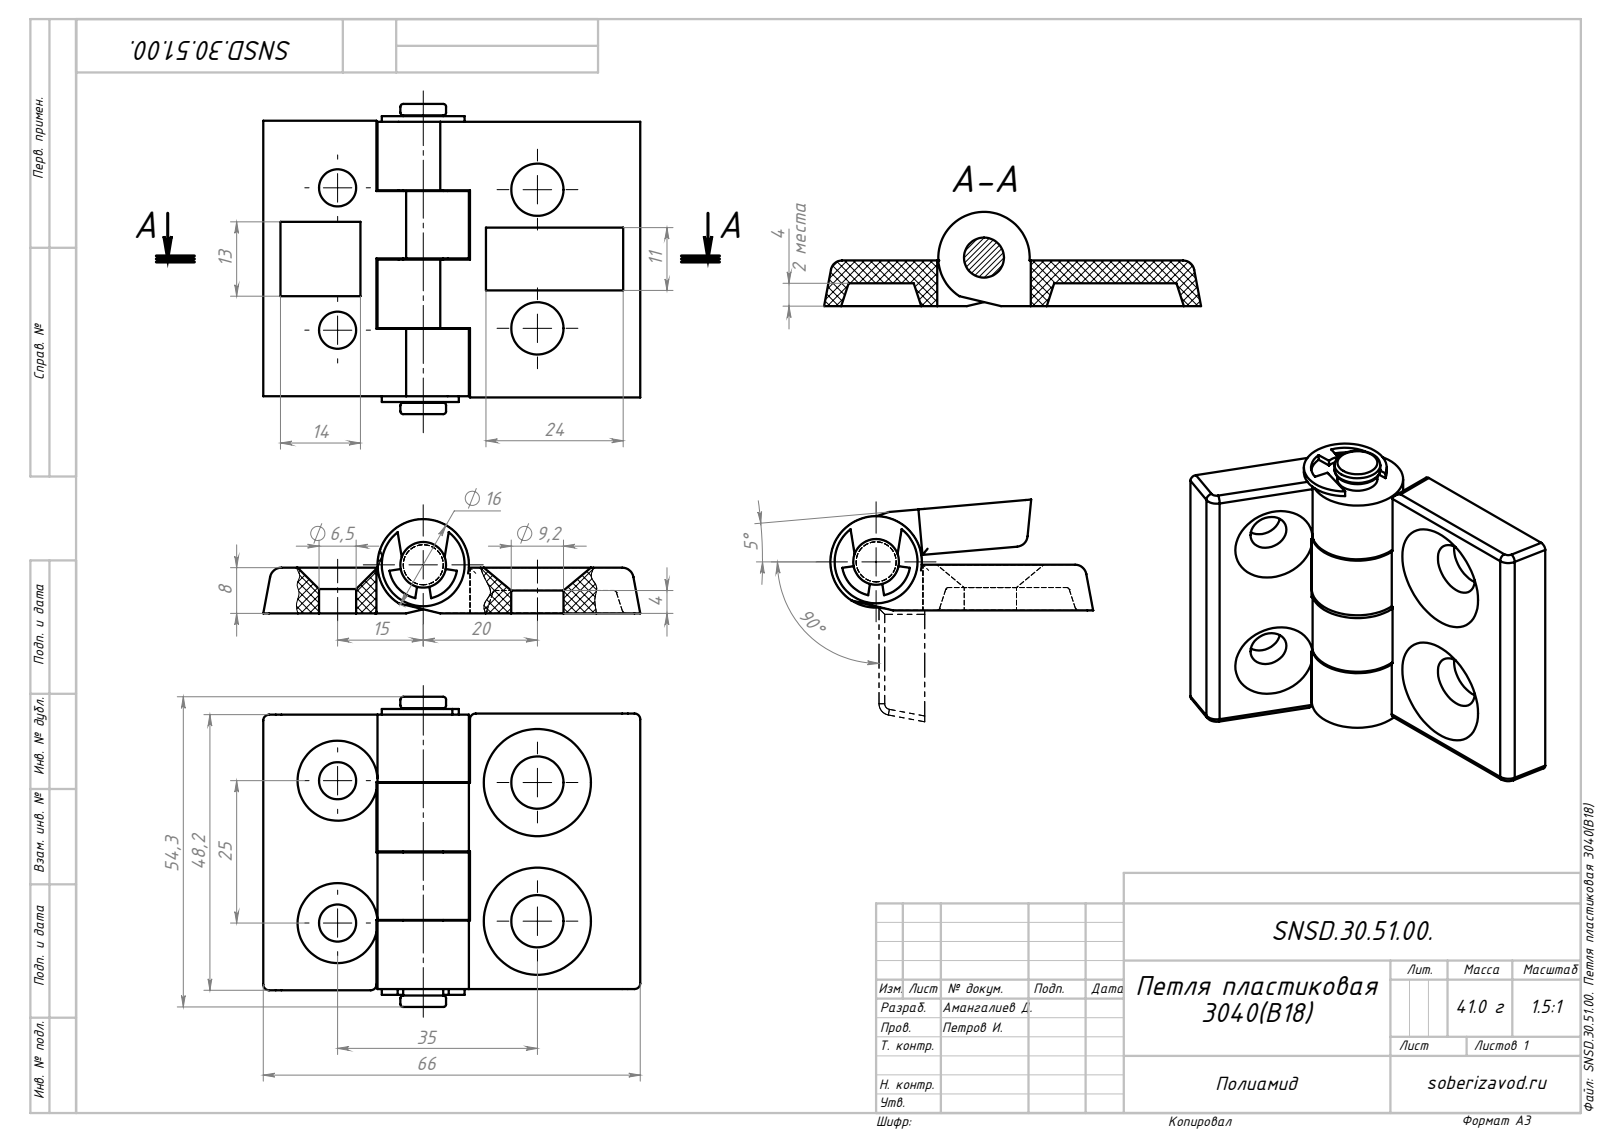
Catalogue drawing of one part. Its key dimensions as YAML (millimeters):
part_name: "SNSD.30.51.00. Петля пластиковая малая часть(B18)_00; SNSD.30.51.00. Петля пластиковая (B18)_00; SNSD.30.51.00. Петля пластиковая 3040(B18); SNSD.30.51.00. Палец (B18)_00 (+1 more)"
step_written_by: "SolidWorks 2022 (AUTOMOTIVE_DESIGN)"
units: millimeters
bodies: {solids: 5, faces: 173, planar: 53, cylindrical: 84, other: 36}
overall_size: [65.97, 54.25, 16.5]
volume: 25051
surface_area: 13411
round_holes:
  - {diameter: 6.5, count: 2}
  - {diameter: 9.15, count: 2}
  - {diameter: 7, count: 1}
round_bosses_or_shafts:
  - {diameter: 16, count: 1}
  - {diameter: 14.5, count: 1}
  - {diameter: 8, count: 1}
partial_cylinders:
  - {radius: 0.5, count: 24}
  - {radius: 1, count: 10}
  - {radius: 2, count: 2}
  - {radius: 6, count: 1}
face_to_face_distances: [8, 24.1, 12, 12.1, 4, 48, 23.9, 11.9, 36.1, 36.2]
hole_center_spacings: [34.97, 42.74, 24.24, 24.9]
